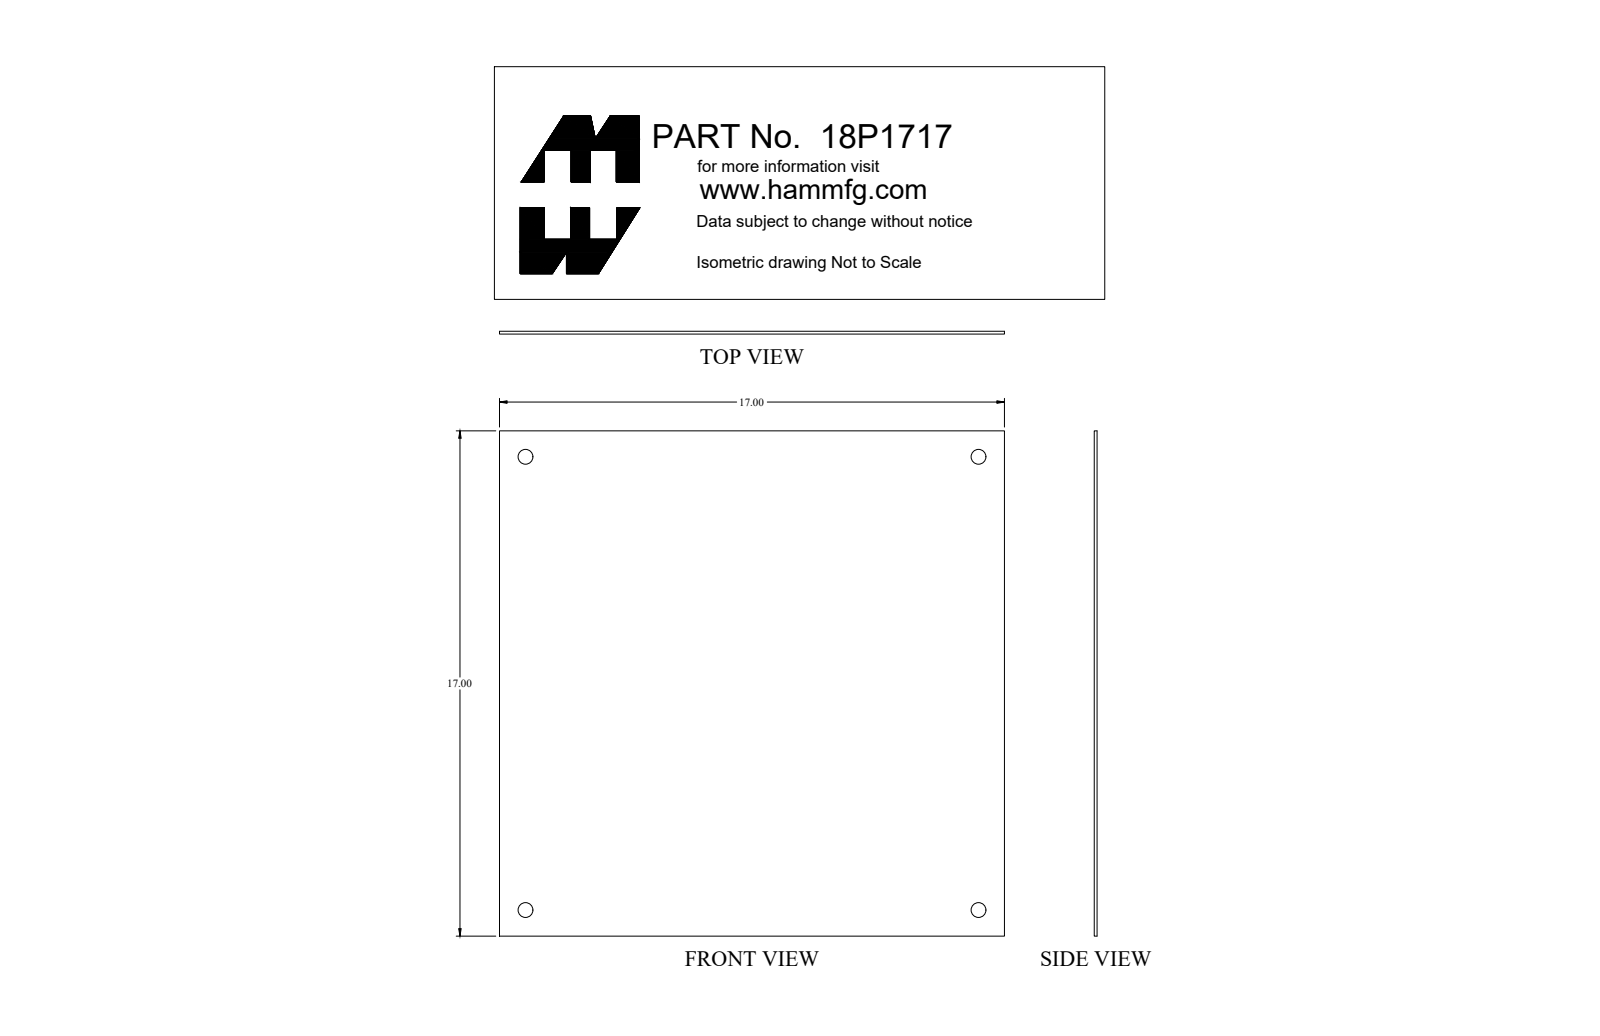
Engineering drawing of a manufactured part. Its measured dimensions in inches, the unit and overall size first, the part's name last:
Units: inches
Overall size (bounding box): 17 × 17 × 0.095
Round holes (diameter × count): ⌀0.5 ×4
Main face-to-face distances: 0.095, 17
Hole centre spacings: 15.25, 21.567
Volume: 27.38 in³ · Surface area: 583.5 in²
Bodies: 1 solid, 14 faces (6 planar, 8 cylindrical, 0 other)
Part name (STEP PRODUCT): 18P1717_Default
STEP written by: SolidWorks 2018 (CONFIG_CONTROL_DESIGN)
